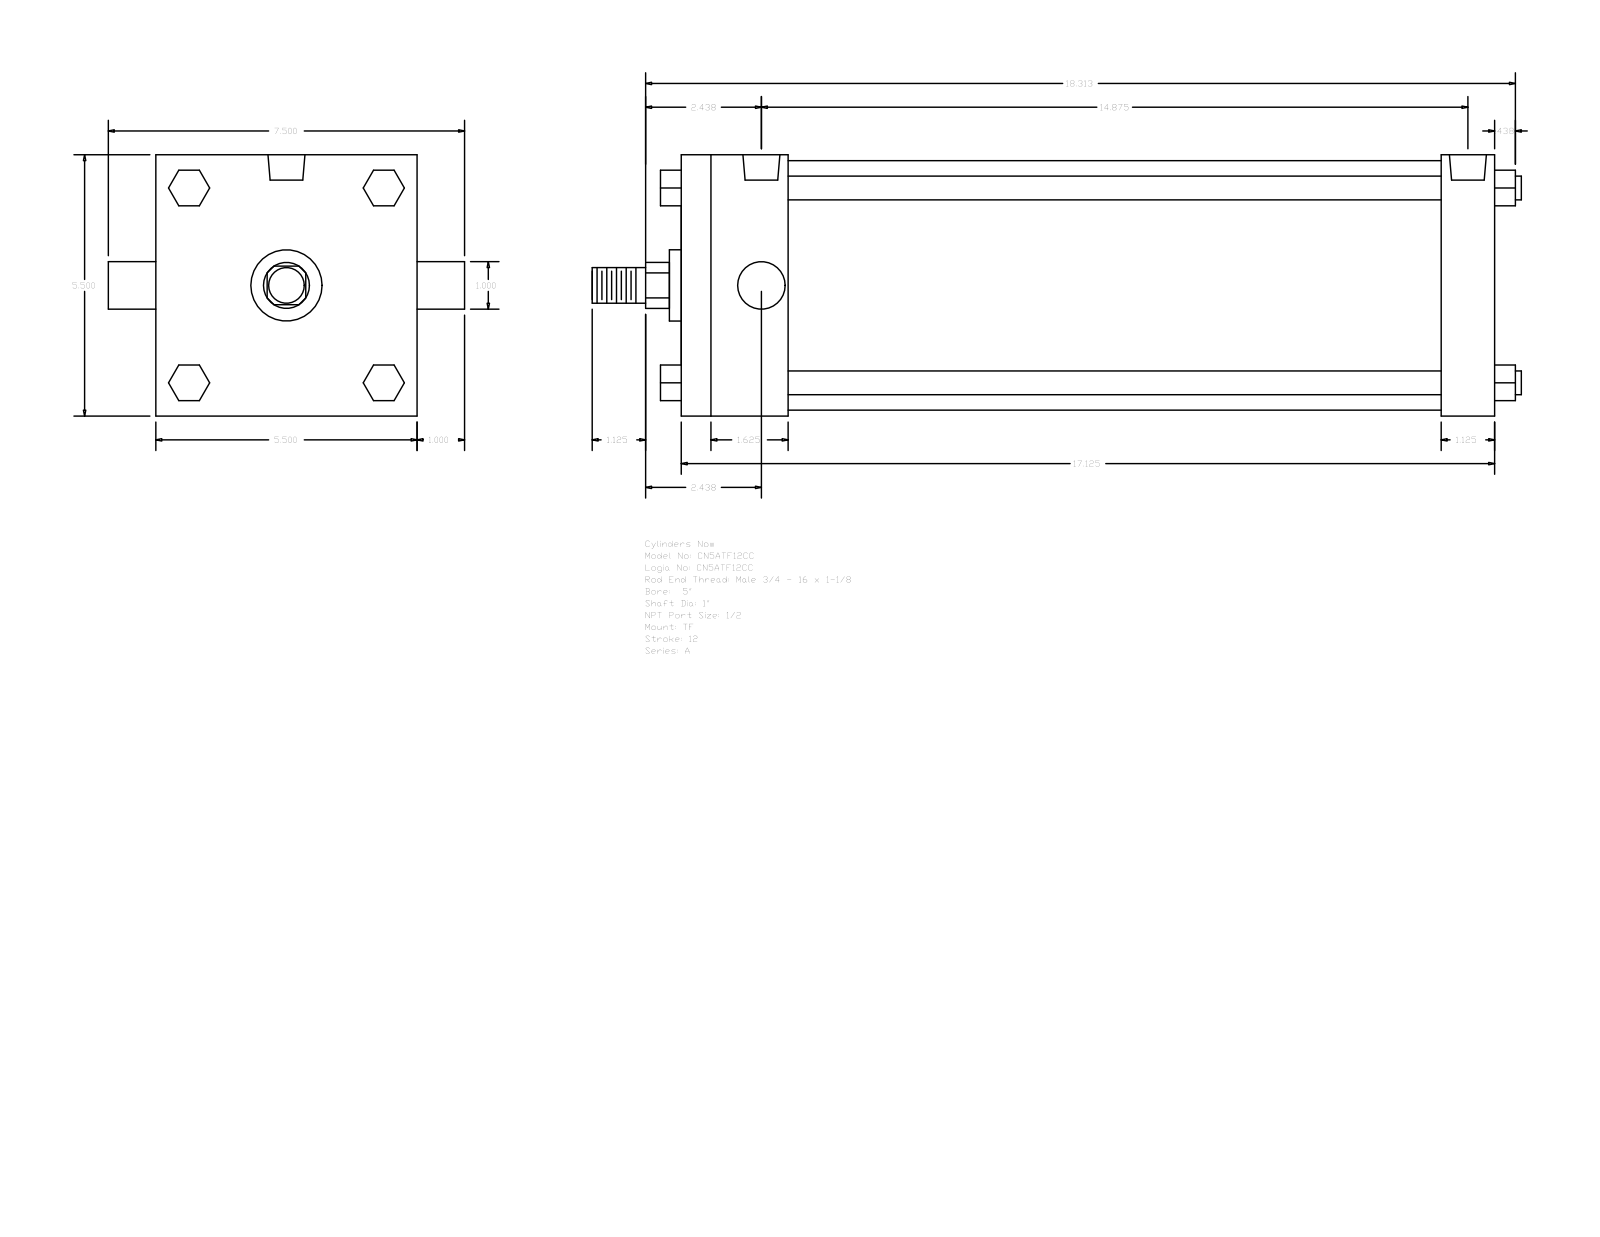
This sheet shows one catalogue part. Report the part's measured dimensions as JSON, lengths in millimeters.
{"part_name": "A_TF__0500_1", "step_written_by": "GSSL Pune (CONFIG_CONTROL_DESIGN)", "units": "millimeters", "bodies": {"solids": 0, "faces": 120, "planar": 92, "cylindrical": 28, "other": 0}, "overall_size": [496.89, 190.5, 139.7], "round_holes": [[8.73, 3], [19.77, 2]], "round_bosses_or_shafts": [[12.7, 4], [25.4, 2], [133.35, 1], [38.1, 1], [19.05, 1]], "partial_cylinders_radius": [[12.29, 1]], "face_to_face_distances": [139.7, 434.97, 28.57, 406.4, 57.15, 349.25, 377.82, 19.05, 52.07, 90.18], "hole_center_spacings": [2.39, 375.44, 373.05, 377.83]}
